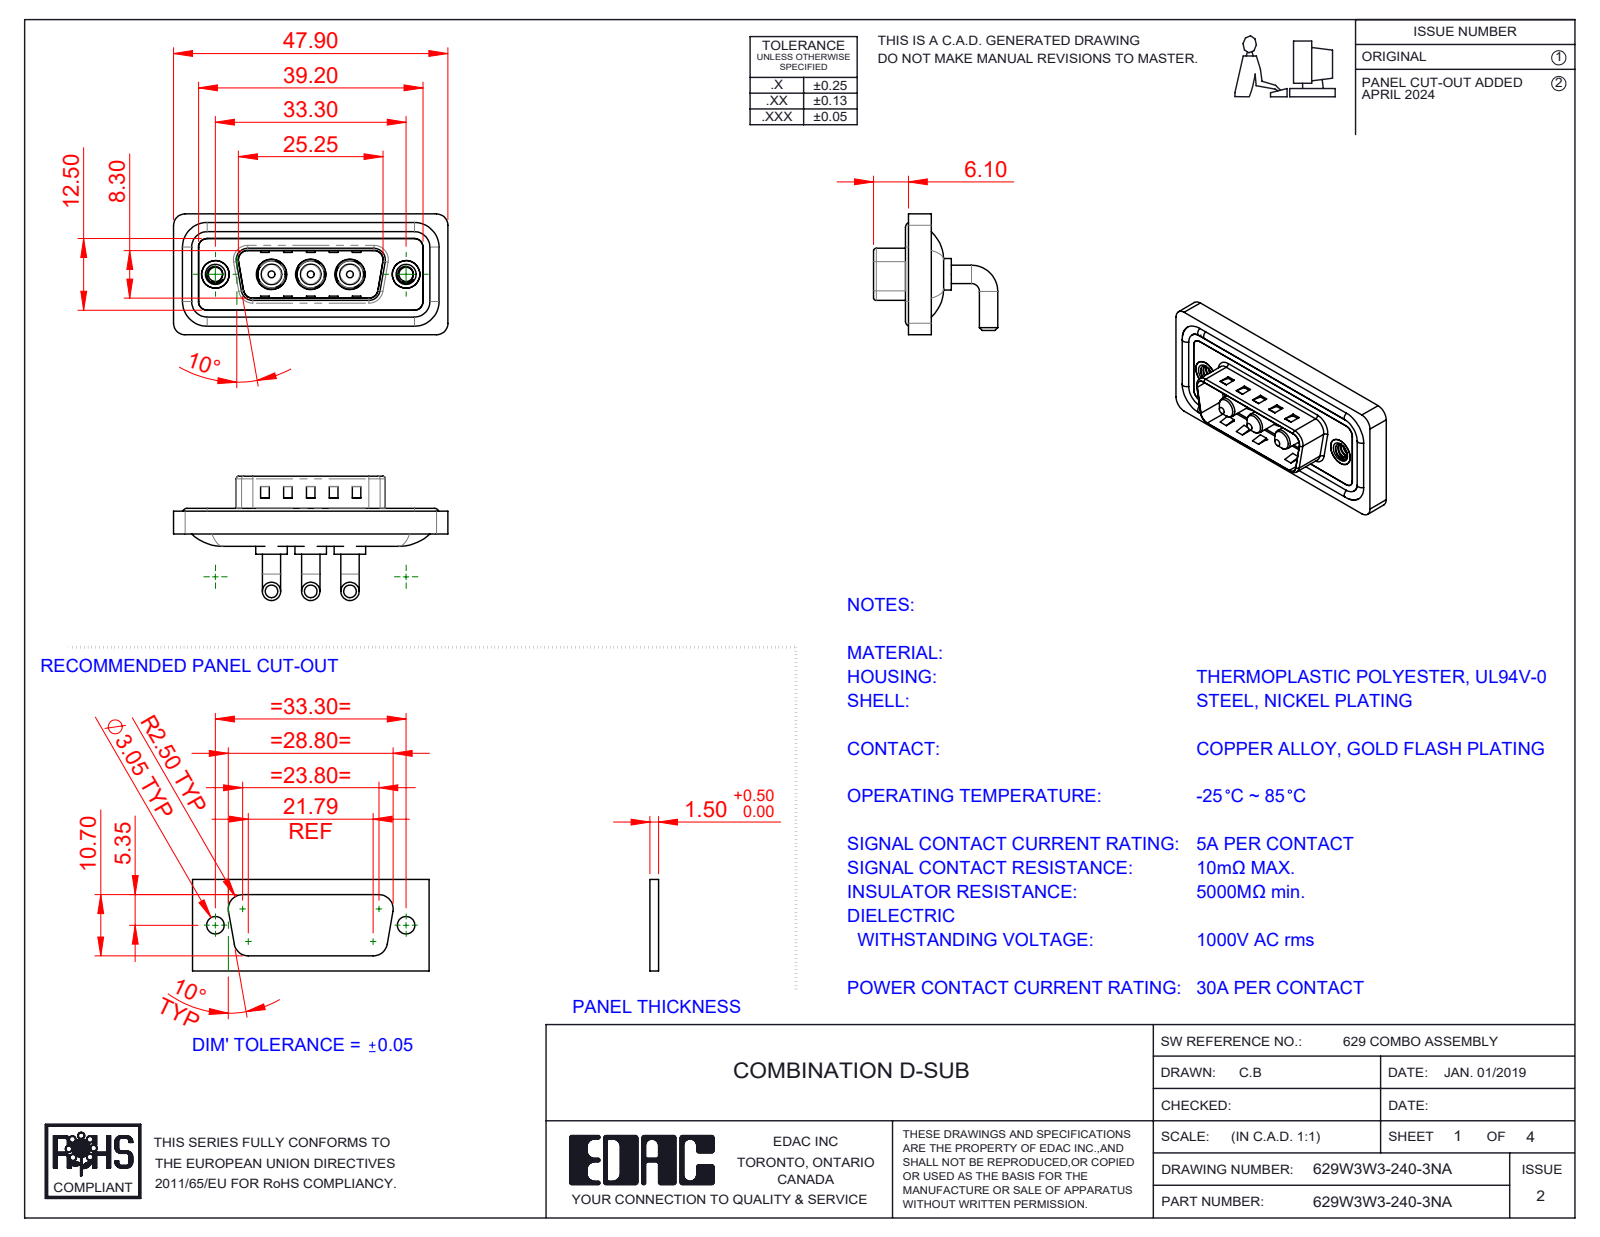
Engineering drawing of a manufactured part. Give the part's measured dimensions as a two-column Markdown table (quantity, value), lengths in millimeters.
| quantity | value |
| --- | --- |
| part name | 629Combo Housing_3W3; Power Pin_30A RA; 629Combo Shell Front_15 Contacts; 629Combo Waterproof Housing_15 Contacts (+3 more) |
| STEP written by | SolidWorks 2023 (CONFIG_CONTROL_DESIGN) |
| units | millimeters |
| bodies | 13 solids, 570 faces (207 planar, 245 cylindrical, 118 other) |
| overall size | 47.9 × 21.7 × 21.1 |
| volume | 5 866 mm³ |
| surface area | 9 095 mm² |
| round holes (diameter × count) | 4.85 × 3, 5.3 × 3, 2.5 × 2, 4 × 2, 4.8 × 2, 5 × 2 |
| round bosses / shafts (diameter × count) | 3.2 × 6, 1.6 × 4, 5.5 × 3, 5.2 × 3, 4.75 × 3, 3.75 × 3, 3.6 × 3, 4.9 × 2 |
| partial cylindrical surfaces (radius × count) | 2 × 20, 1.5 × 18, 0.5 × 8, 1.6 × 8, 0.25 × 4, 0.6 × 4, 0.65 × 4, 0.9 × 4 |
| main face-to-face distances | 0.4, 2.9, 0.8, 1.1, 2.1, 1.6, 3.1, 2.5, 4.5, 3.7 |
| hole center spacings | 6.85, 9.8, 16.65, 23.5, 13.7, 33.3 |
